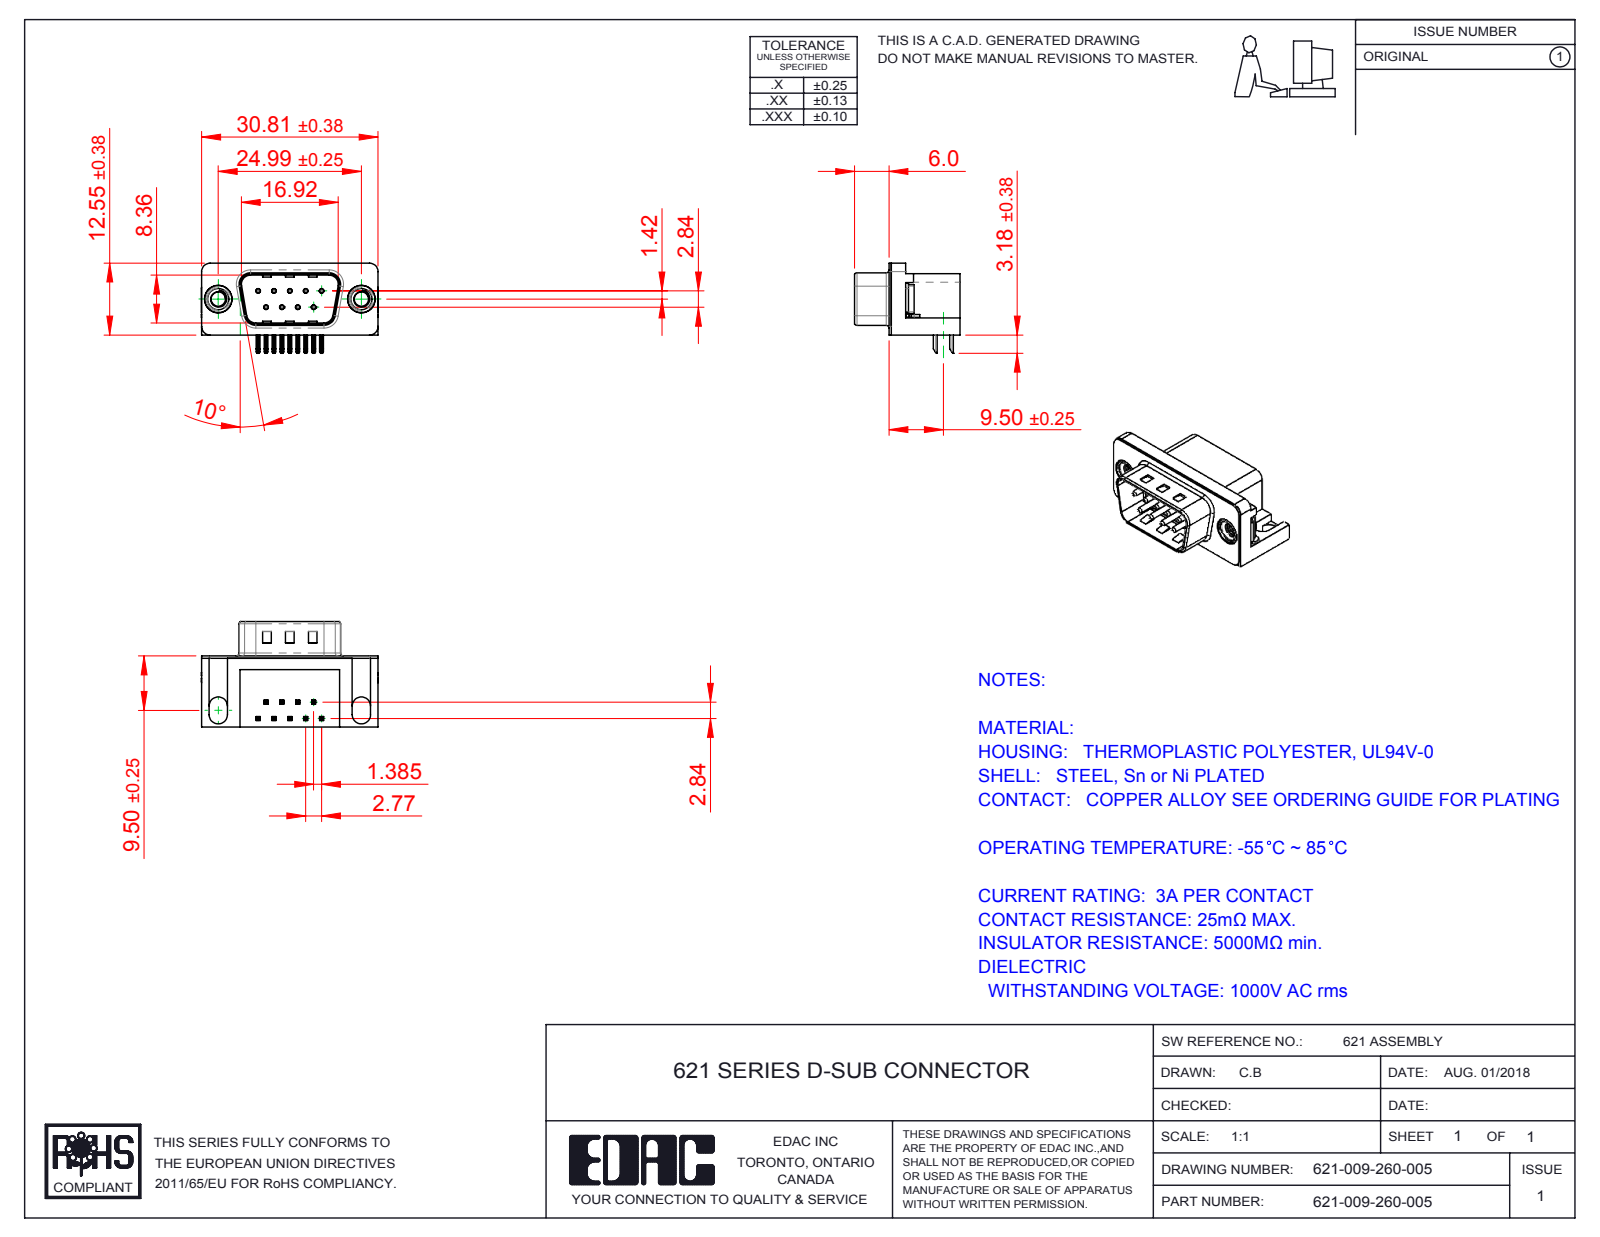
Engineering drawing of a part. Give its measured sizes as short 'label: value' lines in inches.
name: 621-009-260-005; 621 M3 Threaded Rivet; 621 Non Board Mount; 621 Contact Top (+3 more)
written by: SolidWorks 2016 (CONFIG_CONTROL_DESIGN)
unit: in
bodies: 15 solids, 985 faces (571 planar, 315 cylindrical, 99 other)
size: 1.216 × 0.724 × 0.619
volume: 0.196 in³; area: 6.589 in²
holes: 9× ⌀0.014, 9× ⌀0.031, 2× ⌀0.098, 2× ⌀0.157, 2× ⌀0.189, 2× ⌀0.197
bosses: 9× ⌀0.03, 2× ⌀0.193, 2× ⌀0.187, 2× ⌀0.154
rounds: 44× R0.01, 18× R0.005, 16× R0.039, 9× R0.02, 8× R0.059, 8× R0.063, 4× R0.035, 4× R0.079
face distances: 0.016, 0.472, 0.488, 0.407, 0.114, 0.374, 0.098, 0.083, 0.014, 0.421
hole spacings: 0.124, 0.109, 0.218, 0.198, 0.198, 0.327, 0.294, 0.295
